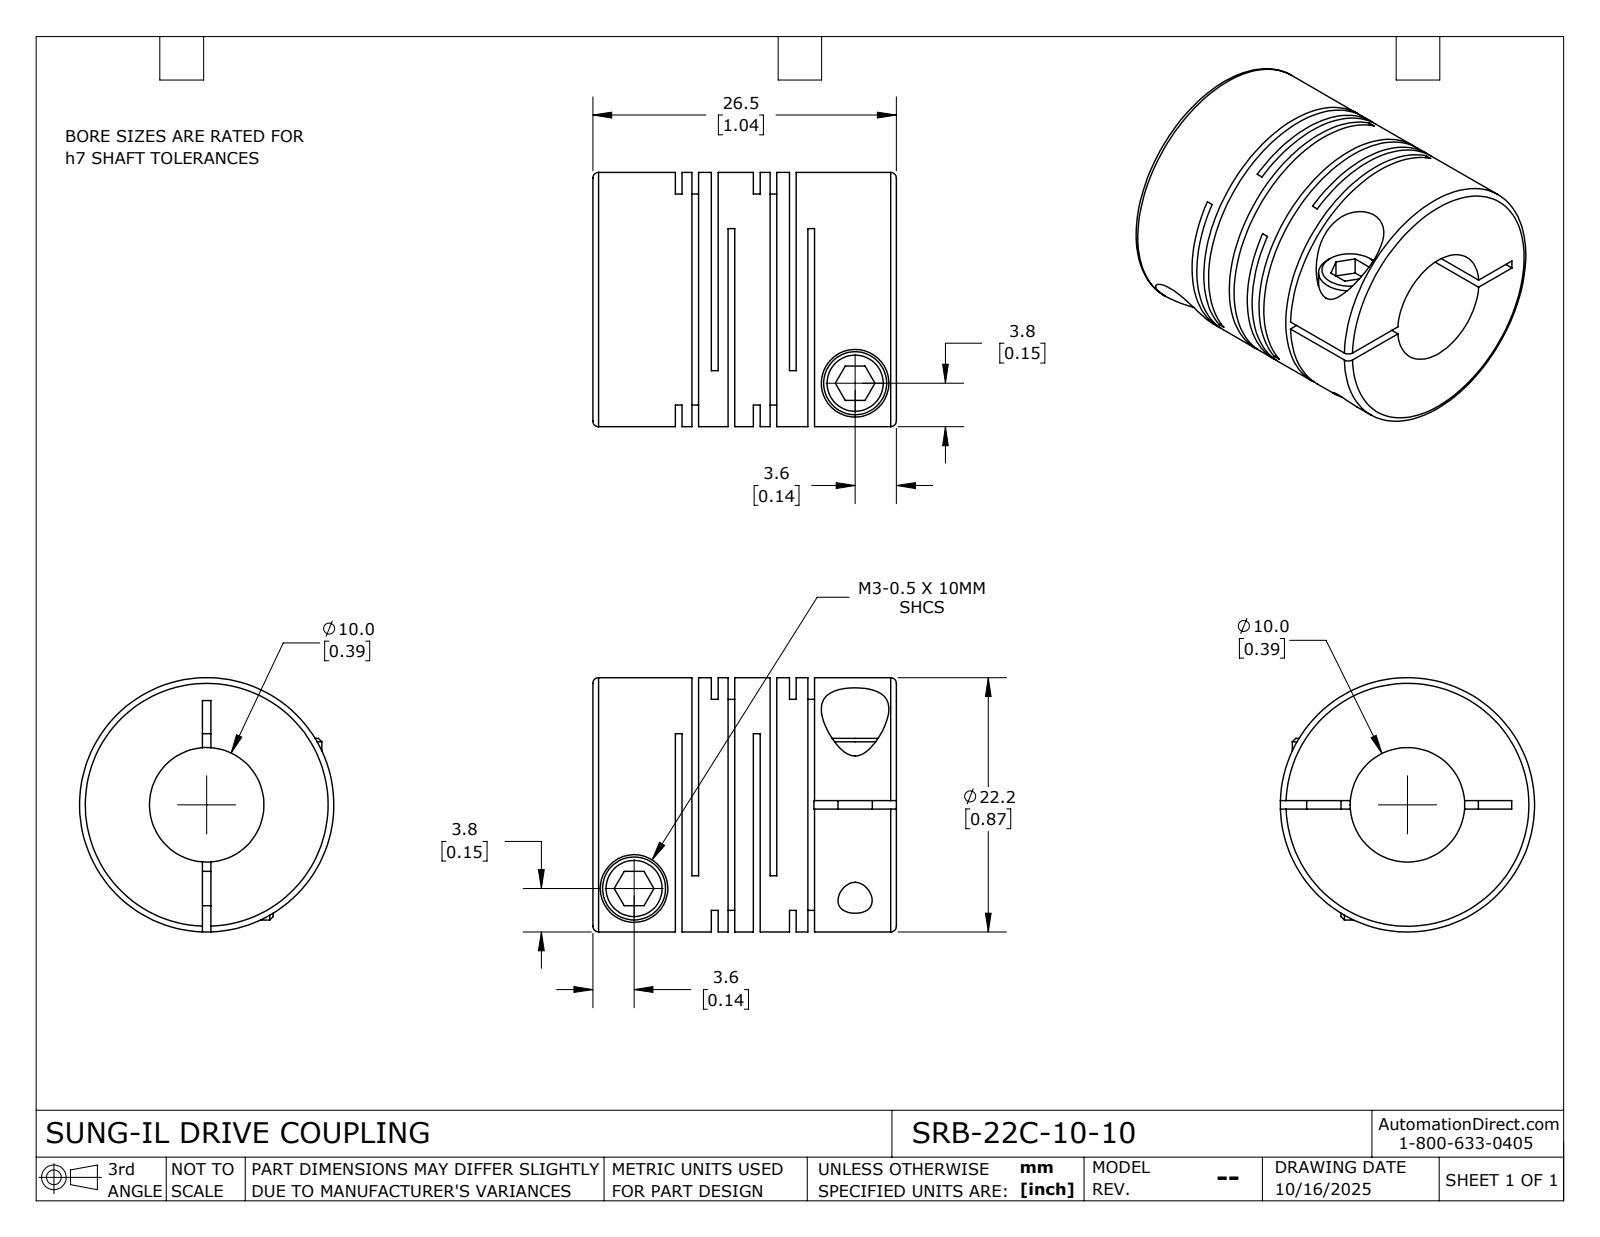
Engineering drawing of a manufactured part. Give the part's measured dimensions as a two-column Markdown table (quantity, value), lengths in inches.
| quantity | value |
| --- | --- |
| part name | SRB-22C-10-10 |
| STEP written by | SolidWorks 2024 (CONFIG_CONTROL_DESIGN) |
| units | inches |
| bodies | 1 solid, 115 faces (60 planar, 42 cylindrical, 13 other) |
| overall size | 1.043 × 0.874 × 0.874 |
| volume | 0.41 in³ |
| surface area | 11.5 in² |
| round holes (diameter × count) | 0.118 × 2, 0.232 × 2, 0.394 × 1 |
| round bosses / shafts (diameter × count) | 0.217 × 2, 0.874 × 1 |
| main face-to-face distances | 0.023, 0.124, 0.269, 0.057, 0.211, 0.144, 0.067, 0.101, 0.245, 0.034 |
